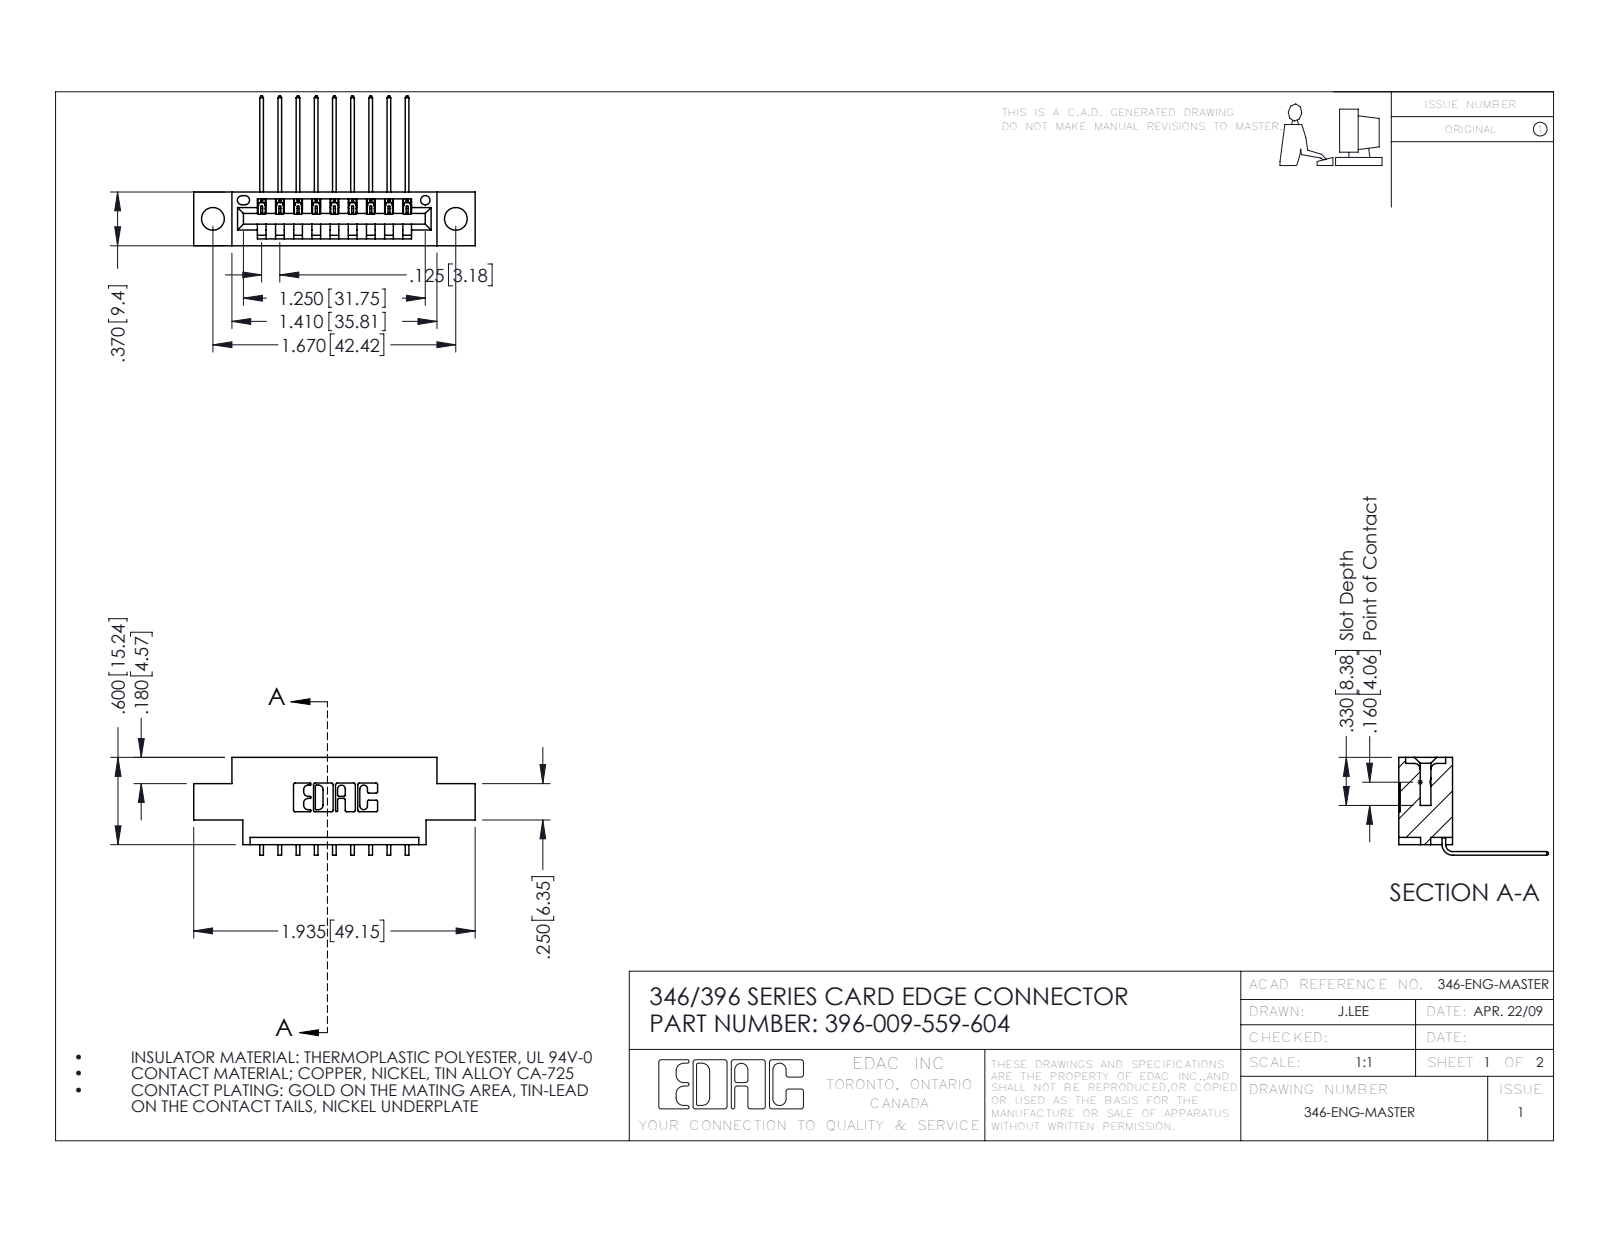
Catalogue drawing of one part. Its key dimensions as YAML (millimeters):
part_name: "345-292-001_558 559 Tail - 1; 346 Part_0.170 Offset - 0.156 Dia-TH; 396-009-559-604"
step_written_by: "SolidWorks 2016 (CONFIG_CONTROL_DESIGN)"
units: millimeters
bodies: {solids: 10, faces: 666, planar: 458, cylindrical: 208, other: 0}
overall_size: [49.1, 26.2, 17.1]
volume: 4260
surface_area: 5119
round_holes:
  - {diameter: 4, count: 2}
  - {diameter: 1.6, count: 1}
partial_cylinders:
  - {radius: 0.3, count: 22}
  - {radius: 0.2, count: 18}
  - {radius: 0.2, count: 6}
  - {radius: 0.8, count: 6}
  - {radius: 0.7, count: 3}
  - {radius: 0.8, count: 2}
  - {radius: 1, count: 2}
  - {radius: 0.4, count: 1}
face_to_face_distances: [6.4, 9.4, 1.2, 8.2, 0.6, 1.8, 3.8, 5.6, 2.5, 4.4]
hole_center_spacings: [6.2, 37.2, 42.4]
